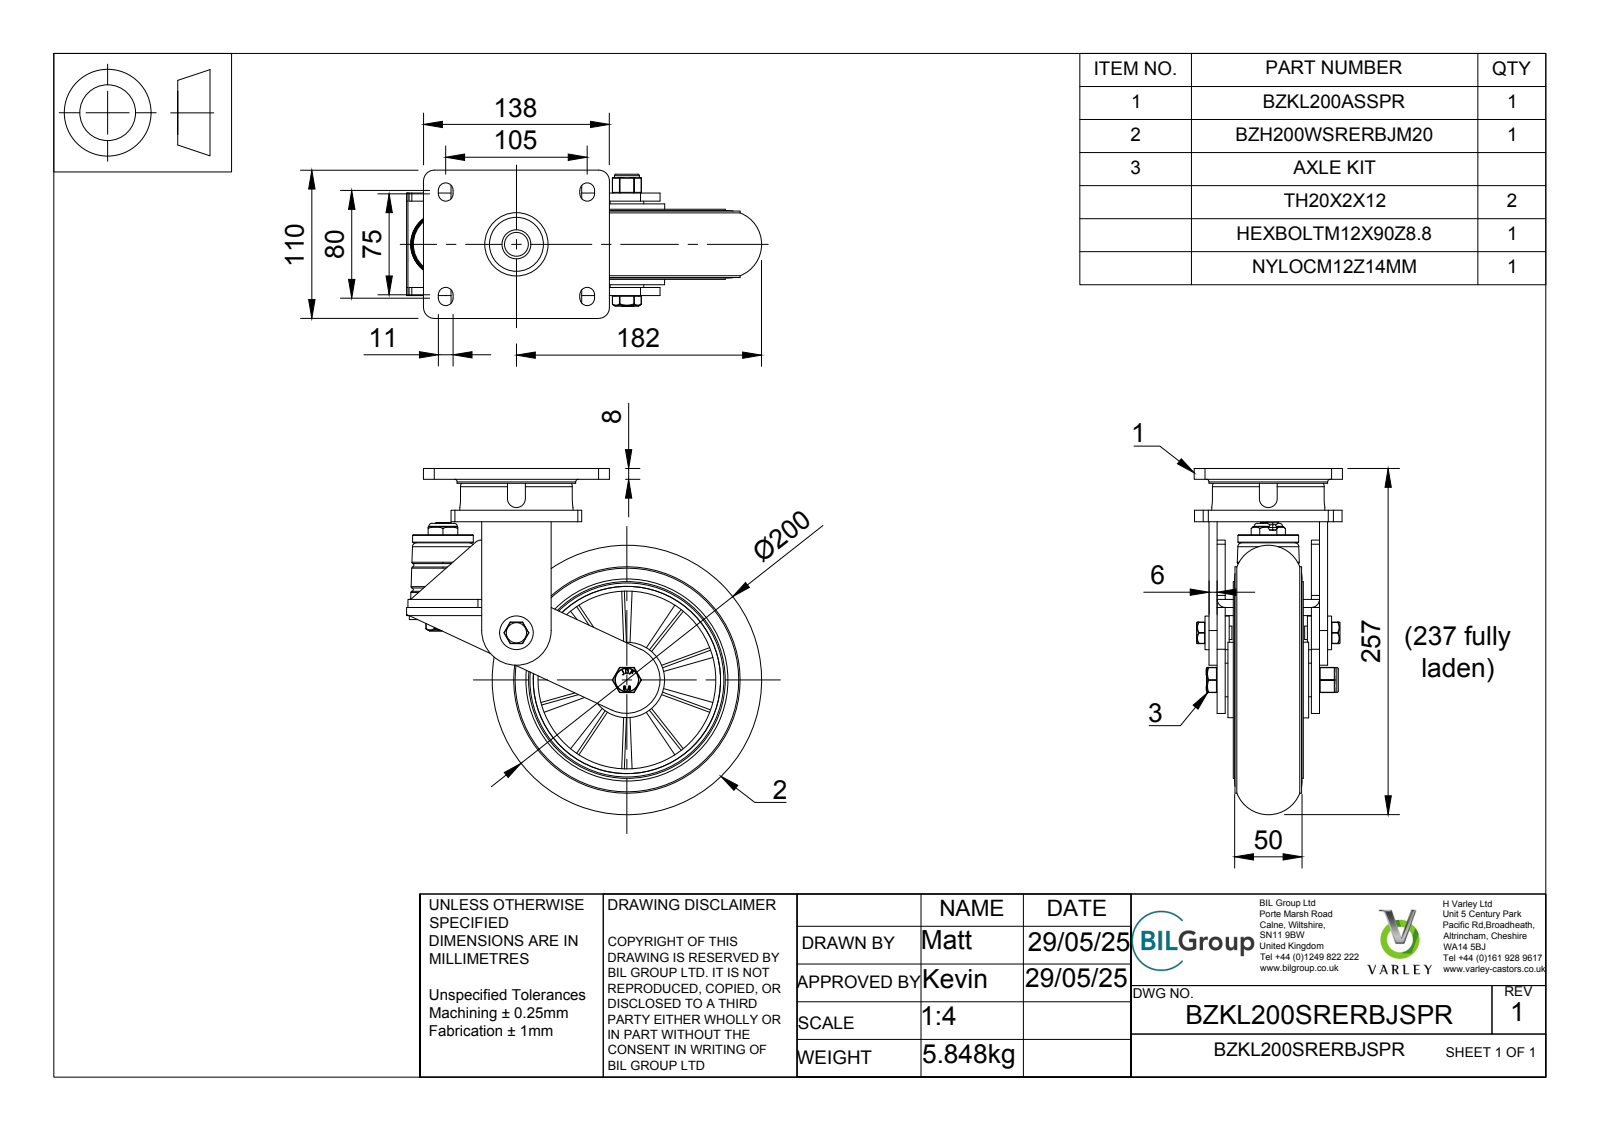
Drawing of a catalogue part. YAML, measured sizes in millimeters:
part_name: "BZKL200SRERBJSPR v3; BZKL200ASSPR v1; FABRICATED STEEL TOP PLATE; FABRICATED STEEL FORKS (+6 more)"
step_written_by: "Autodesk Translation Framework v14.10.0.0 (AUTOMOTIVE_DESIGN)"
units: millimeters
bodies: {solids: 50, faces: 1374, planar: 542, cylindrical: 310, other: 522}
overall_size: [263.51, 257, 110]
volume: 1514000
surface_area: 419565
round_holes:
  - {diameter: 12, count: 2}
  - {diameter: 47, count: 2}
  - {diameter: 10, count: 1}
  - {diameter: 12.1, count: 1}
  - {diameter: 12.2, count: 1}
  - {diameter: 14, count: 1}
  - {diameter: 20, count: 1}
  - {diameter: 28.5, count: 1}
  - {diameter: 30.8, count: 1}
  - {diameter: 40.3, count: 1}
  - {diameter: 40.5, count: 1}
  - {diameter: 42, count: 1}
round_bosses_or_shafts:
  - {diameter: 25, count: 2}
  - {diameter: 168, count: 1}
  - {diameter: 146, count: 1}
  - {diameter: 88, count: 1}
  - {diameter: 84, count: 1}
  - {diameter: 56.2, count: 1}
  - {diameter: 56, count: 1}
  - {diameter: 50, count: 1}
partial_cylinders:
  - {radius: 0.5, count: 36}
  - {radius: 5.5, count: 8}
  - {radius: 6, count: 5}
  - {radius: 0.47, count: 4}
  - {radius: 0.9, count: 4}
  - {radius: 4, count: 4}
  - {radius: 8, count: 4}
  - {radius: 3, count: 3}
face_to_face_distances: [6, 76, 70, 12, 8, 31.5, 14.25, 2, 47.75, 82]
hole_center_spacings: [54.51, 89.16]
